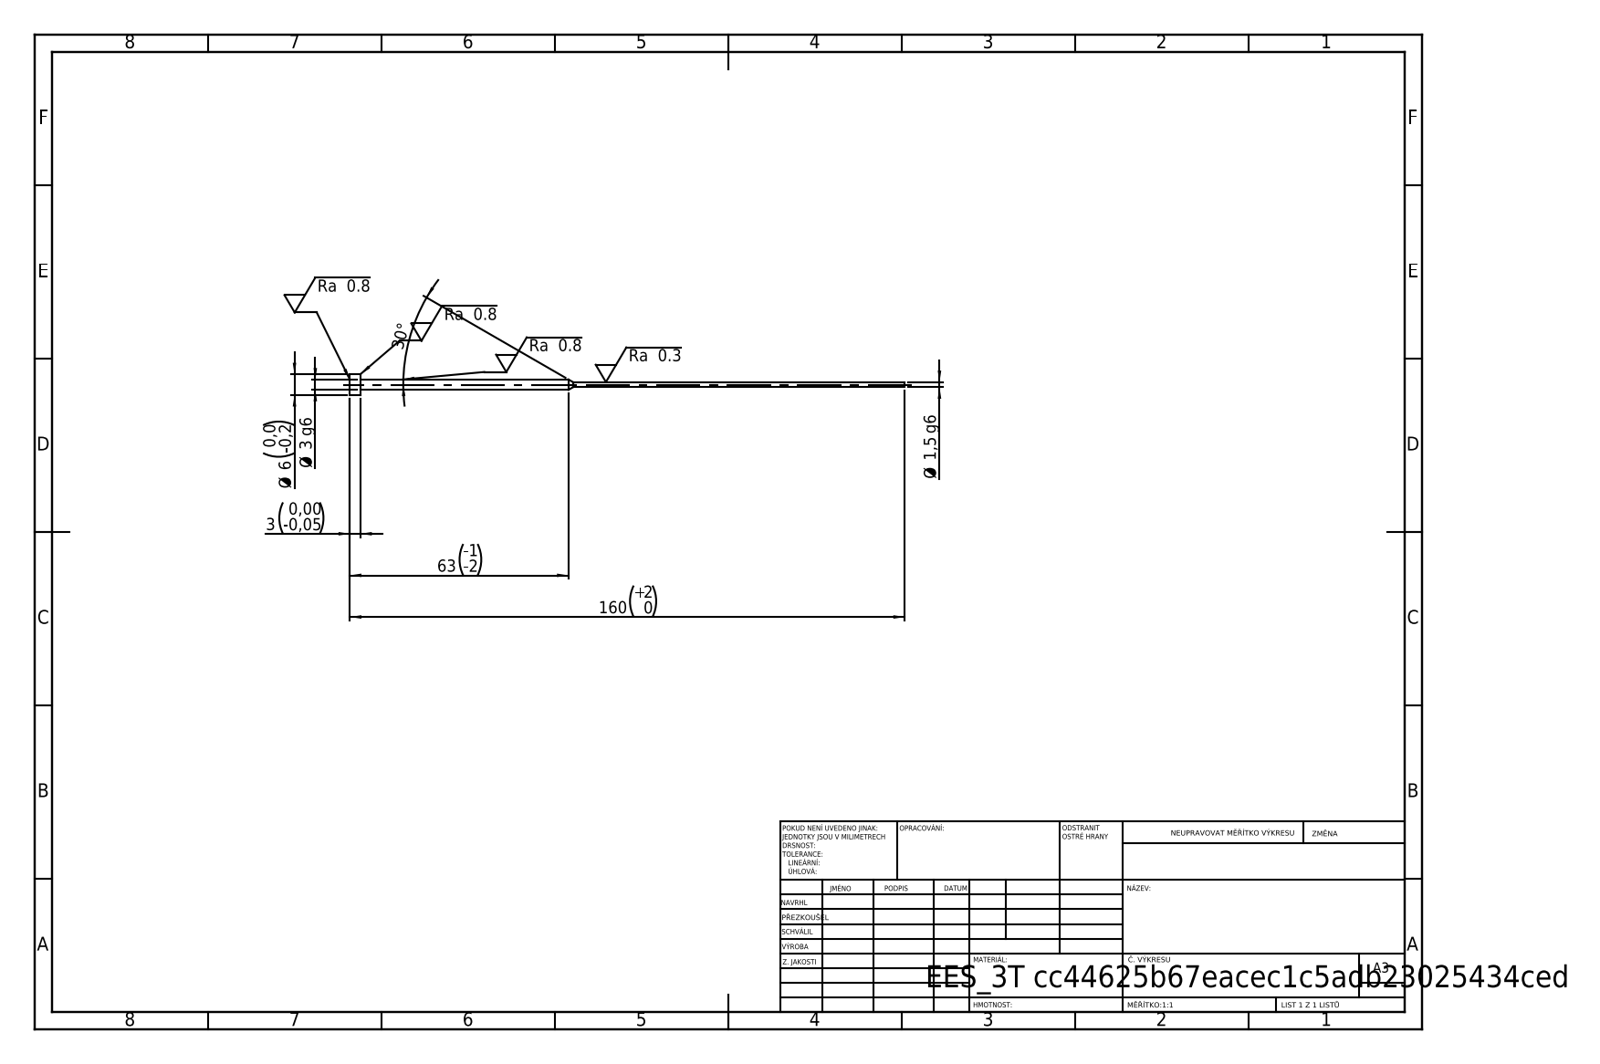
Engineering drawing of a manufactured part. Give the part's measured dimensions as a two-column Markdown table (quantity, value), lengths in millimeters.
| quantity | value |
| --- | --- |
| STEP written by | SolidWorks 2019 (CONFIG_CONTROL_DESIGN) |
| units | millimeters |
| bodies | 1 solid, 11 faces (3 planar, 6 cylindrical, 2 other) |
| overall size | 160 × 6 × 6 |
| volume | 683 mm³ |
| surface area | 1 135 mm² |
| round bosses / shafts (diameter × count) | 6 × 1, 3 × 1, 1.5 × 1 |
| main face-to-face distances | 3, 157, 160 |
